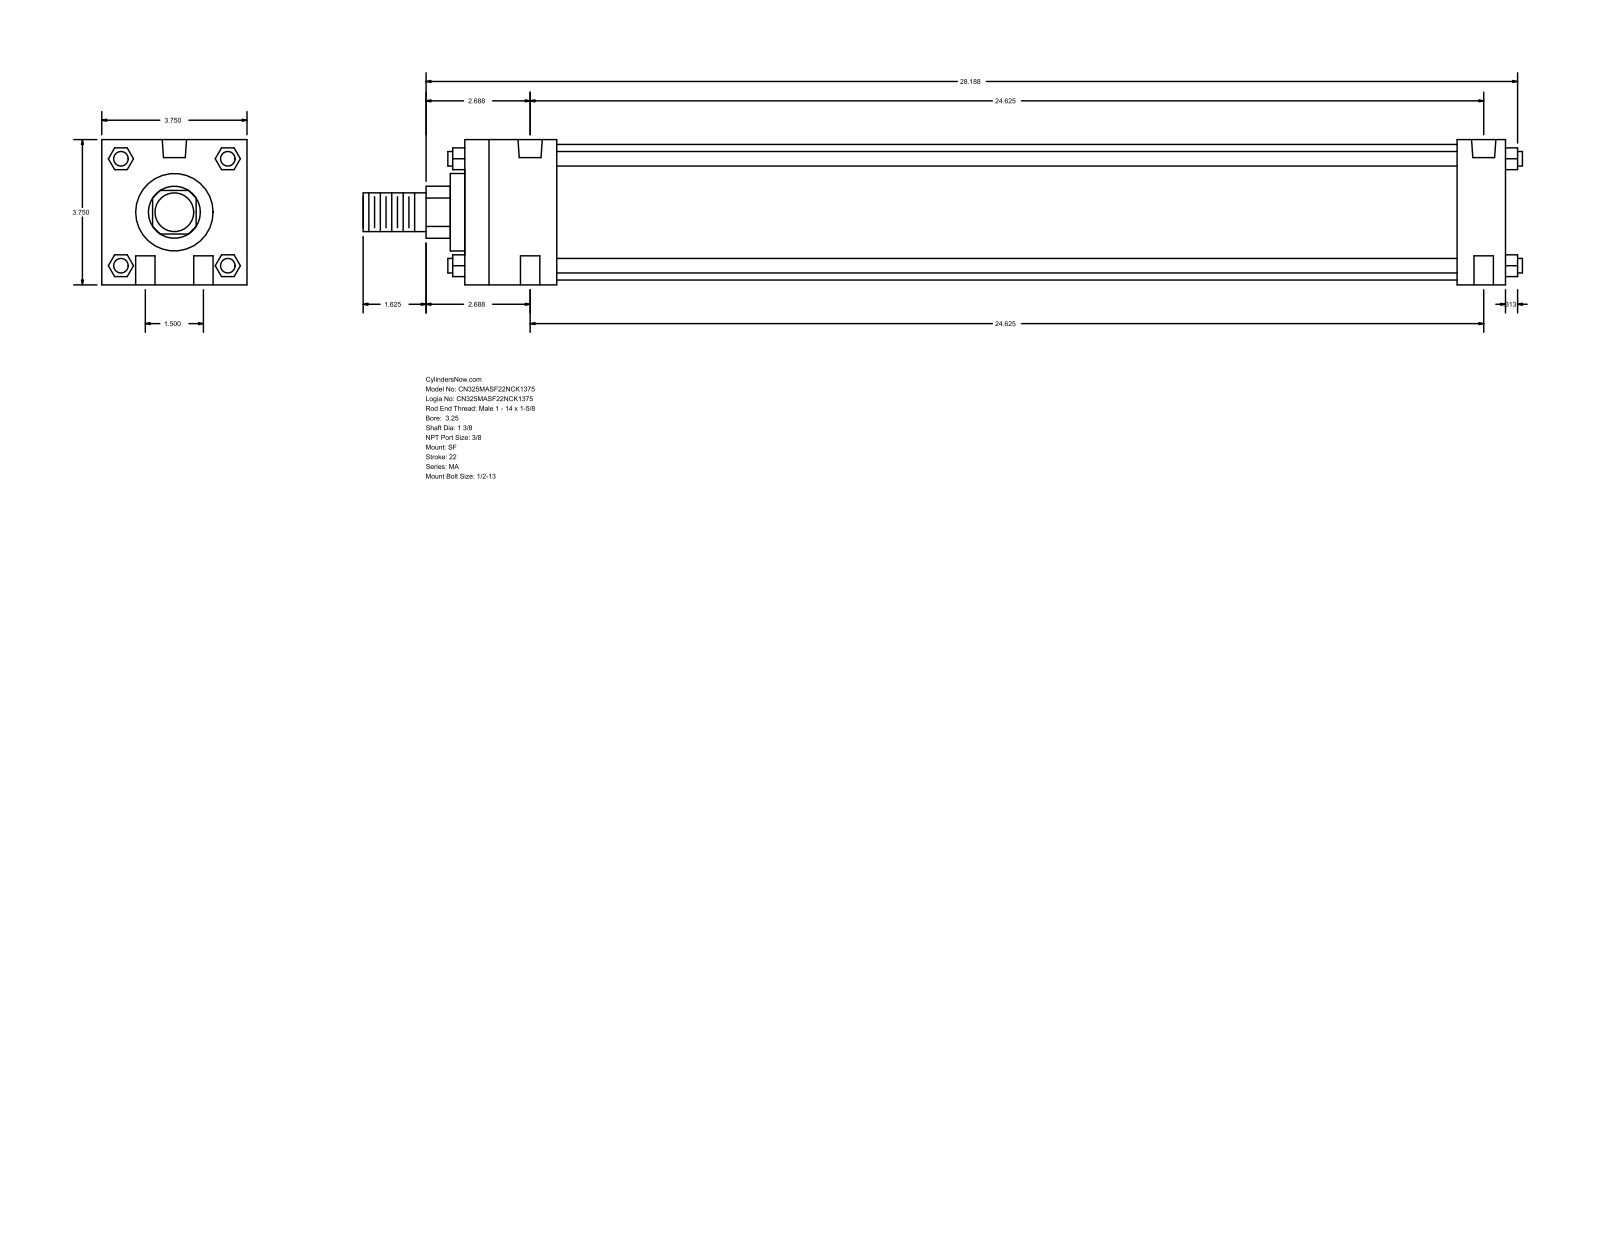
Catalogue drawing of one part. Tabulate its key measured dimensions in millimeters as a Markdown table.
| quantity | value |
| --- | --- |
| part name | MA_SF__0325_1.375 |
| STEP written by | GSSL Pune (CONFIG_CONTROL_DESIGN) |
| units | millimeters |
| bodies | 0 solids, 124 faces (94 planar, 30 cylindrical, 0 other) |
| overall size | 760.41 × 95.25 × 95.25 |
| round holes (diameter × count) | 12.7 × 4, 11.11 × 2, 15.93 × 2 |
| round bosses / shafts (diameter × count) | 9.53 × 4, 88.9 × 1, 50.8 × 1, 34.92 × 1, 25.4 × 1 |
| partial cylindrical surfaces (radius × count) | 17.06 × 1 |
| main face-to-face distances | 95.24, 682.62, 650.87, 31.75, 60.32, 590.55, 622.3, 9.52, 69.84, 660.39 |
| hole center spacings | 19.05, 625.77, 625.48, 38.1, 626.64, 615.95 |
